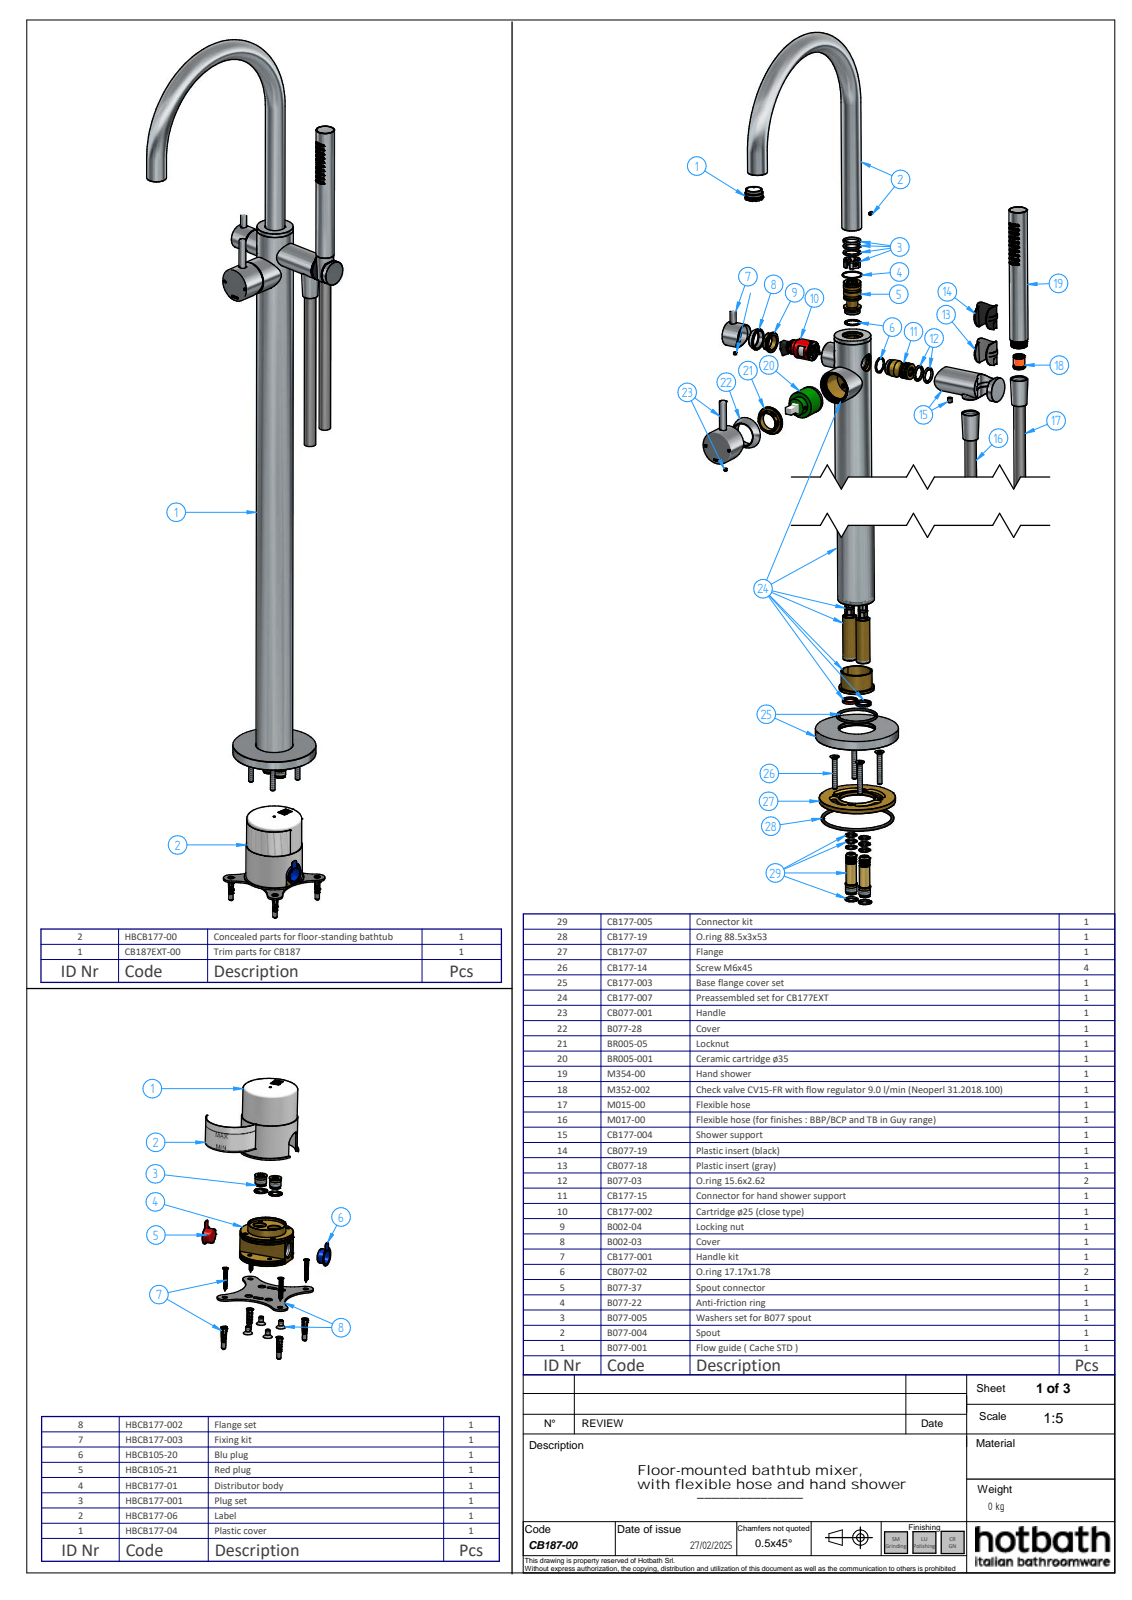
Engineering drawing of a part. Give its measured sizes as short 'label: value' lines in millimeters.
name: CB187EXT-00; B002-03; CB077-18; CB177-004_oa_0 (+8 more)
written by: Solid Edge (AUTOMOTIVE_DESIGN)
unit: mm
bodies: 23 solids, 1288 faces (418 planar, 337 cylindrical, 533 other)
size: 1059.2 × 292.5 × 172.3
volume: 631 476 mm³; area: 442 198 mm²
holes: 41× ⌀3.2, 4× ⌀23, 2× ⌀4.2, 2× ⌀16.5, 2× ⌀18.63, 2× ⌀27, 2× ⌀41, 1× ⌀3.3, 1× ⌀4, 1× ⌀5, 1× ⌀6.2, 1× ⌀7.15
bosses: 4× ⌀15, 2× ⌀32, 2× ⌀26, 2× ⌀8, 1× ⌀109, 1× ⌀45.6, 1× ⌀44, 1× ⌀37
rounds: 20× R0.2, 4× R0.35, 4× R3.5, 3× R0.59, 2× R0.22, 2× R0.23, 2× R0.28, 2× R0.42
face distances: 2, 748, 3.5, 750, 1, 10, 12, 760, 3.6, 758
hole spacings: 7.21, 12.65, 6, 12, 18.44, 4, 18, 24.33
